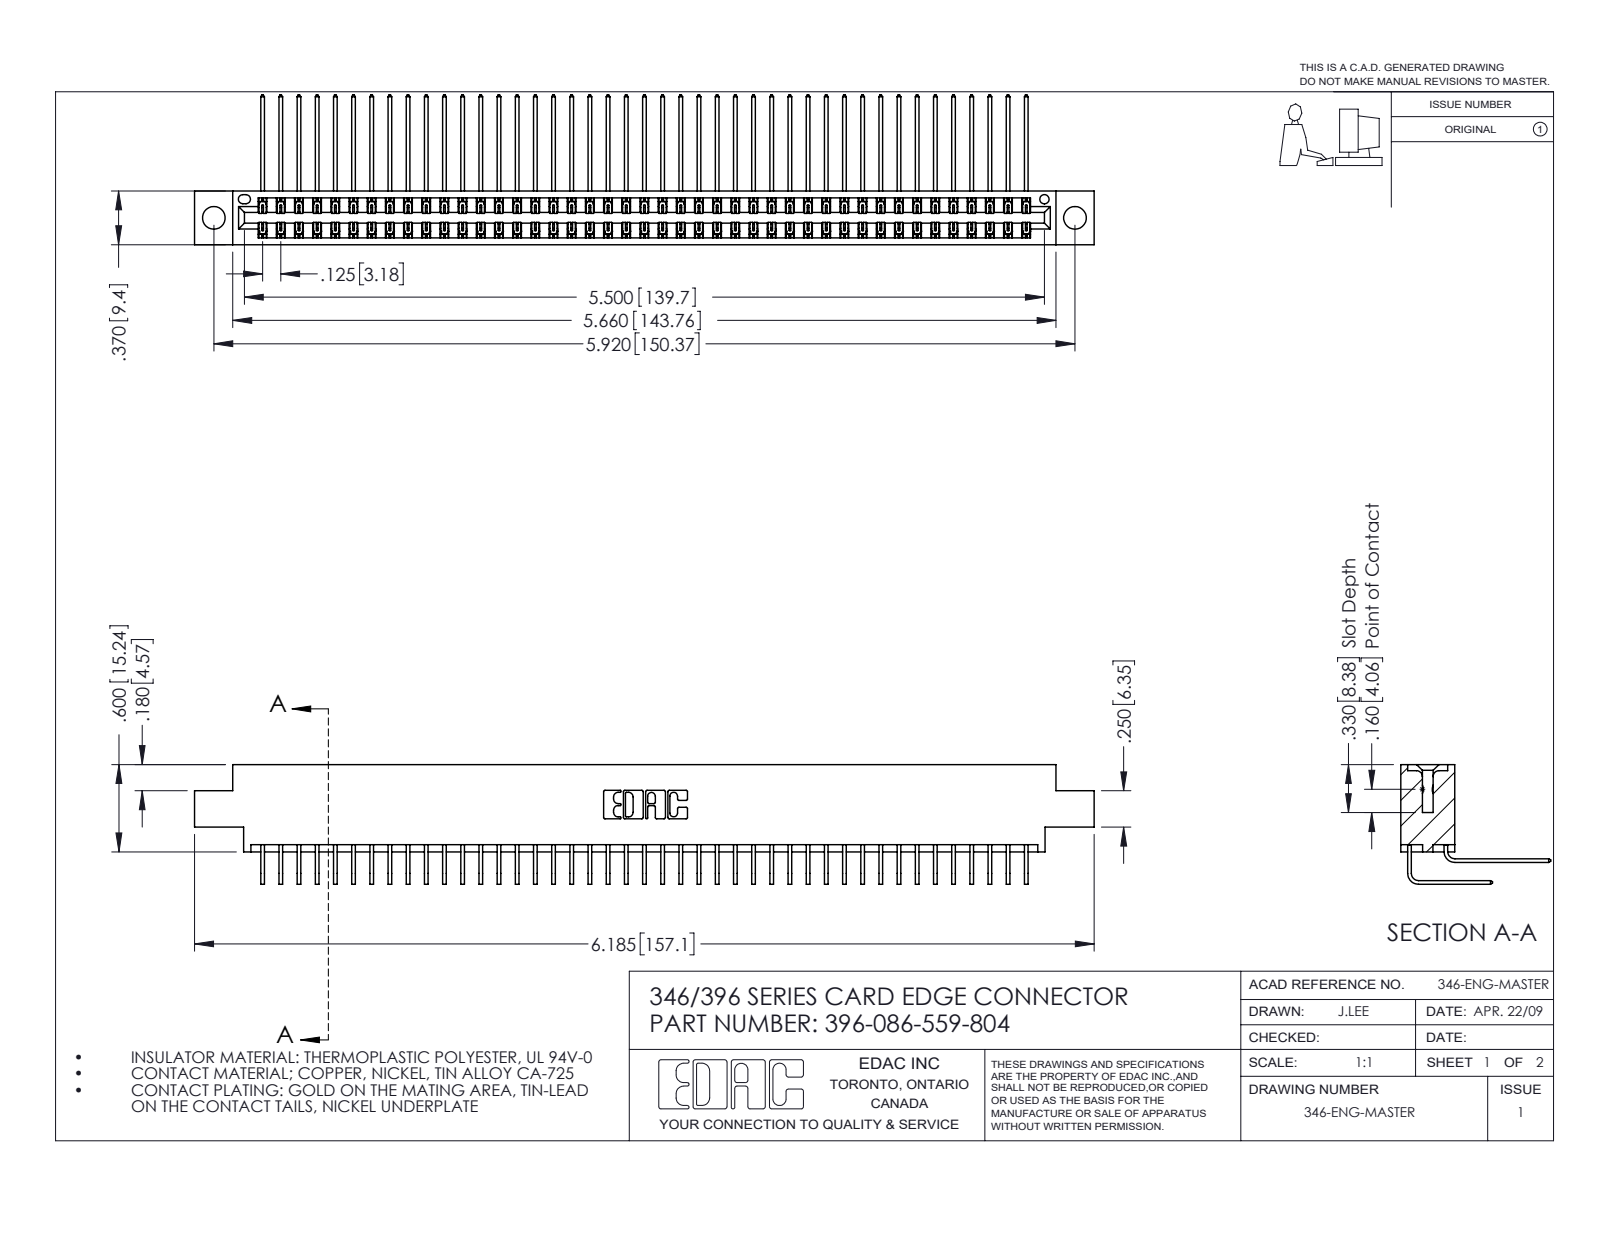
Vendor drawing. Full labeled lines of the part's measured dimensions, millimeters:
Part name (STEP PRODUCT): 345-292-001_558 559 Tail - 1; 396-086-559-804; 345-292-001_559 Tail - 2; 346 Part_0.170 Offset - 0.156 Dia-TH
STEP written by: SolidWorks 2016 (CONFIG_CONTROL_DESIGN)
Units: millimetres
Bodies: 87 solids, 4770 faces (3262 planar, 1508 cylindrical, 0 other)
Overall size (bounding box): 157.1 × 26.2 × 20.9
Volume: 15 600 mm³ · Surface area: 23 810 mm²
Round holes (diameter × count): ⌀4 ×2, ⌀1.6 ×1
Partial cylindrical surfaces — rounded edges, fillets, slot ends (radius × count): R0.2 ×129, R0.3 ×22, R0.2 ×6, R0.8 ×6, R0.7 ×3, R0.4 ×2, R0.6 ×2, R0.6 ×2
Main face-to-face distances: 1.2, 8.2, 0.6, 9.4, 6.4, 1.8, 7.6, 7, 3.8, 5.6
Hole centre spacings: 6.2, 145.1, 150.4
